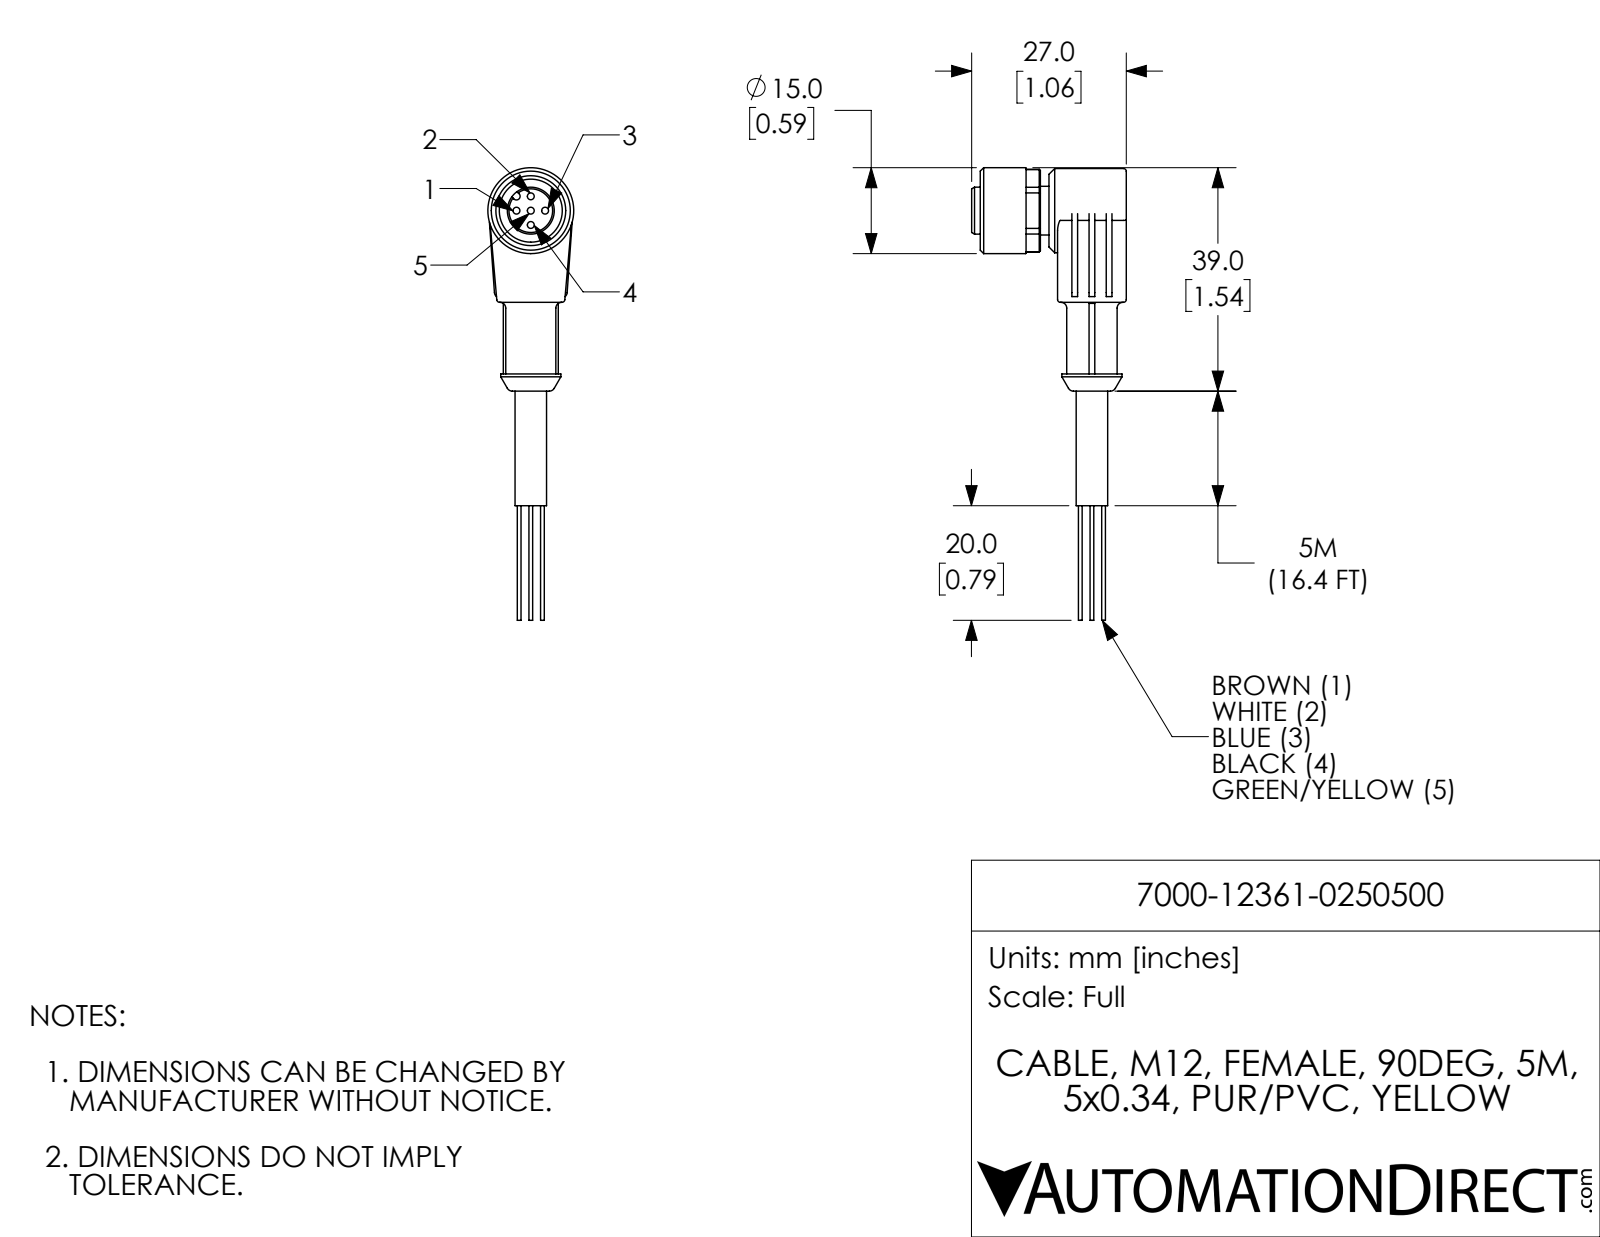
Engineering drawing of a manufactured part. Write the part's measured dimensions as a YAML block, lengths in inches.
part_name: "7000-12361-0250500"
step_written_by: "SolidWorks 2017 (AUTOMOTIVE_DESIGN)"
units: inches
bodies: {solids: 1, faces: 155, planar: 66, cylindrical: 61, other: 28}
overall_size: [3.11, 1.063, 0.591]
volume: 0.417
surface_area: 5.916
round_holes:
  - {diameter: 0.047, count: 5}
  - {diameter: 0.189, count: 1}
  - {diameter: 0.433, count: 1}
round_bosses_or_shafts:
  - {diameter: 0.026, count: 5}
  - {diameter: 0.591, count: 1}
  - {diameter: 0.579, count: 1}
  - {diameter: 0.413, count: 1}
  - {diameter: 0.346, count: 1}
  - {diameter: 0.335, count: 1}
  - {diameter: 0.323, count: 1}
  - {diameter: 0.217, count: 1}
partial_cylinders:
  - {radius: 0.02, count: 8}
  - {radius: 0.039, count: 2}
  - {radius: 0.026, count: 1}
  - {radius: 0.283, count: 1}
face_to_face_distances: [0.472, 0.059, 0.118, 0.531, 0.591, 0.217, 0.374, 0.236, 0.315, 0.492]
hole_center_spacings: [0.098, 0.139, 0.197]
